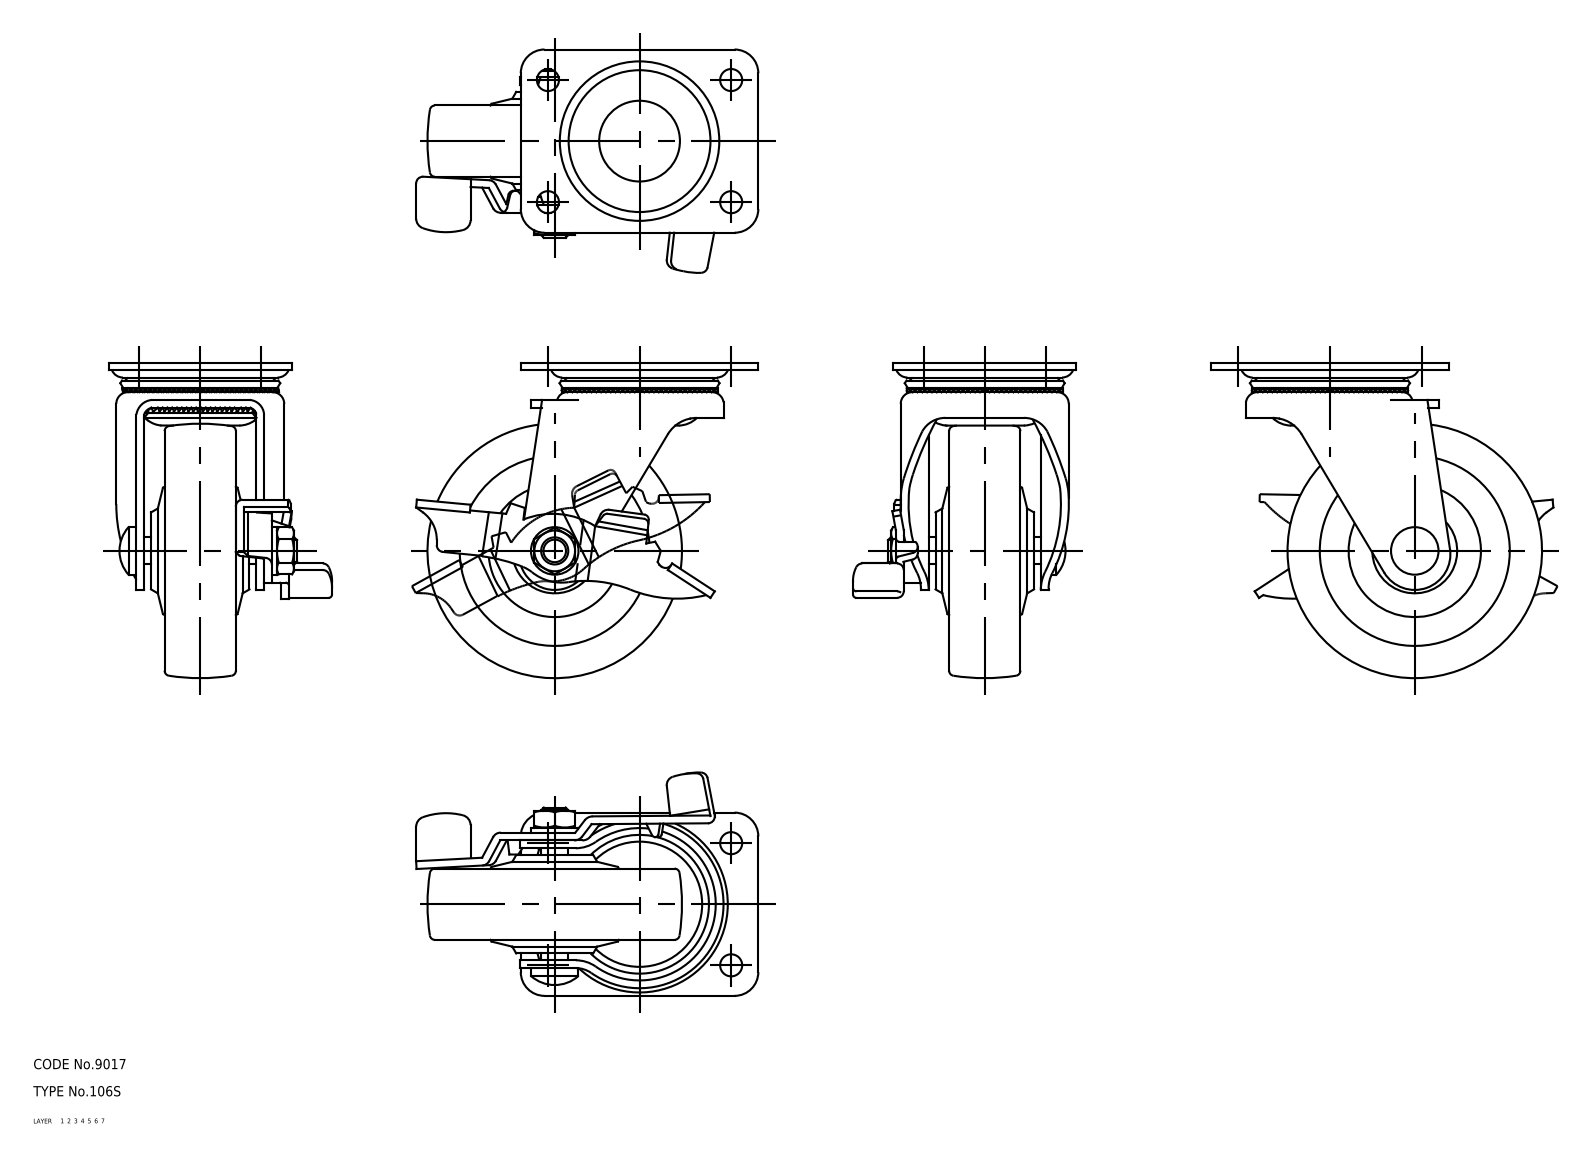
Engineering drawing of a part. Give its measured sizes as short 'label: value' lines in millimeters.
name: wheel; mounting plate; main shaft; lever (+2 more)
written by: CADfix (AUTOMOTIVE_DESIGN)
unit: mm
bodies: 6 solids, 286 faces (0 planar, 0 cylindrical, 286 other)
size: 100.84 × 93 × 65.82
volume: 139 075 mm³; area: 43 947 mm²
